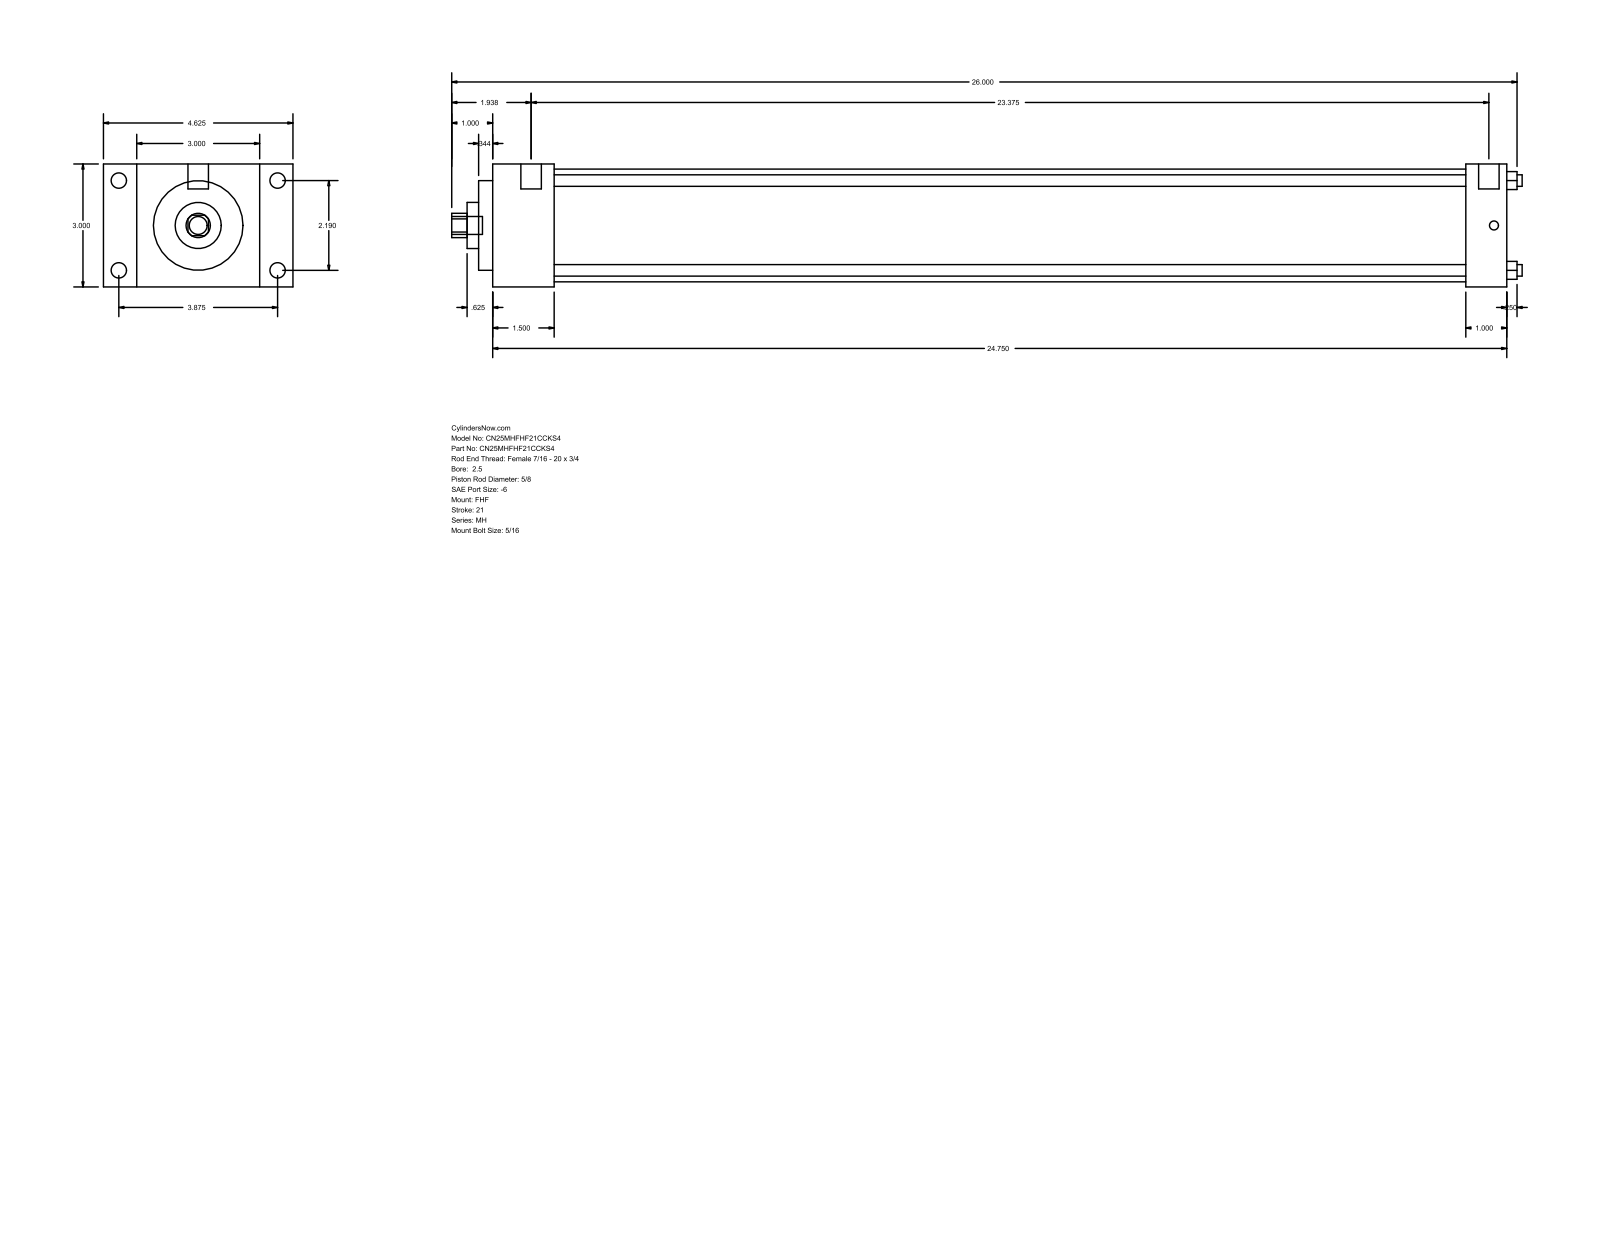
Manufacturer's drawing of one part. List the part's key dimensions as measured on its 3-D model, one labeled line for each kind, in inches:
Part name (STEP PRODUCT): MH_FHF__0250_0.625
STEP written by: GSSL Pune (CONFIG_CONTROL_DESIGN)
Units: inches
Bodies: 0 solids, 90 faces (61 planar, 29 cylindrical, 0 other)
Overall size (bounding box): 26.125 × 4.625 × 3
Round holes (diameter × count): ⌀0.281 ×4, ⌀0.625 ×1, ⌀1.125 ×1, ⌀2.187 ×1, ⌀2.75 ×1
Round bosses / shafts (diameter × count): ⌀0.375 ×4, ⌀0.219 ×4, ⌀0.5 ×2, ⌀0.437 ×1
Partial cylindrical surfaces — rounded edges, fillets, slot ends (radius × count): R0.297 ×1
Main face-to-face distances: 3, 24.75, 1.5, 23.25, 0.813, 3.813, 4.625, 1, 23.75, 22.25
Hole centre spacings: 1.548, 2.19, 3.097
